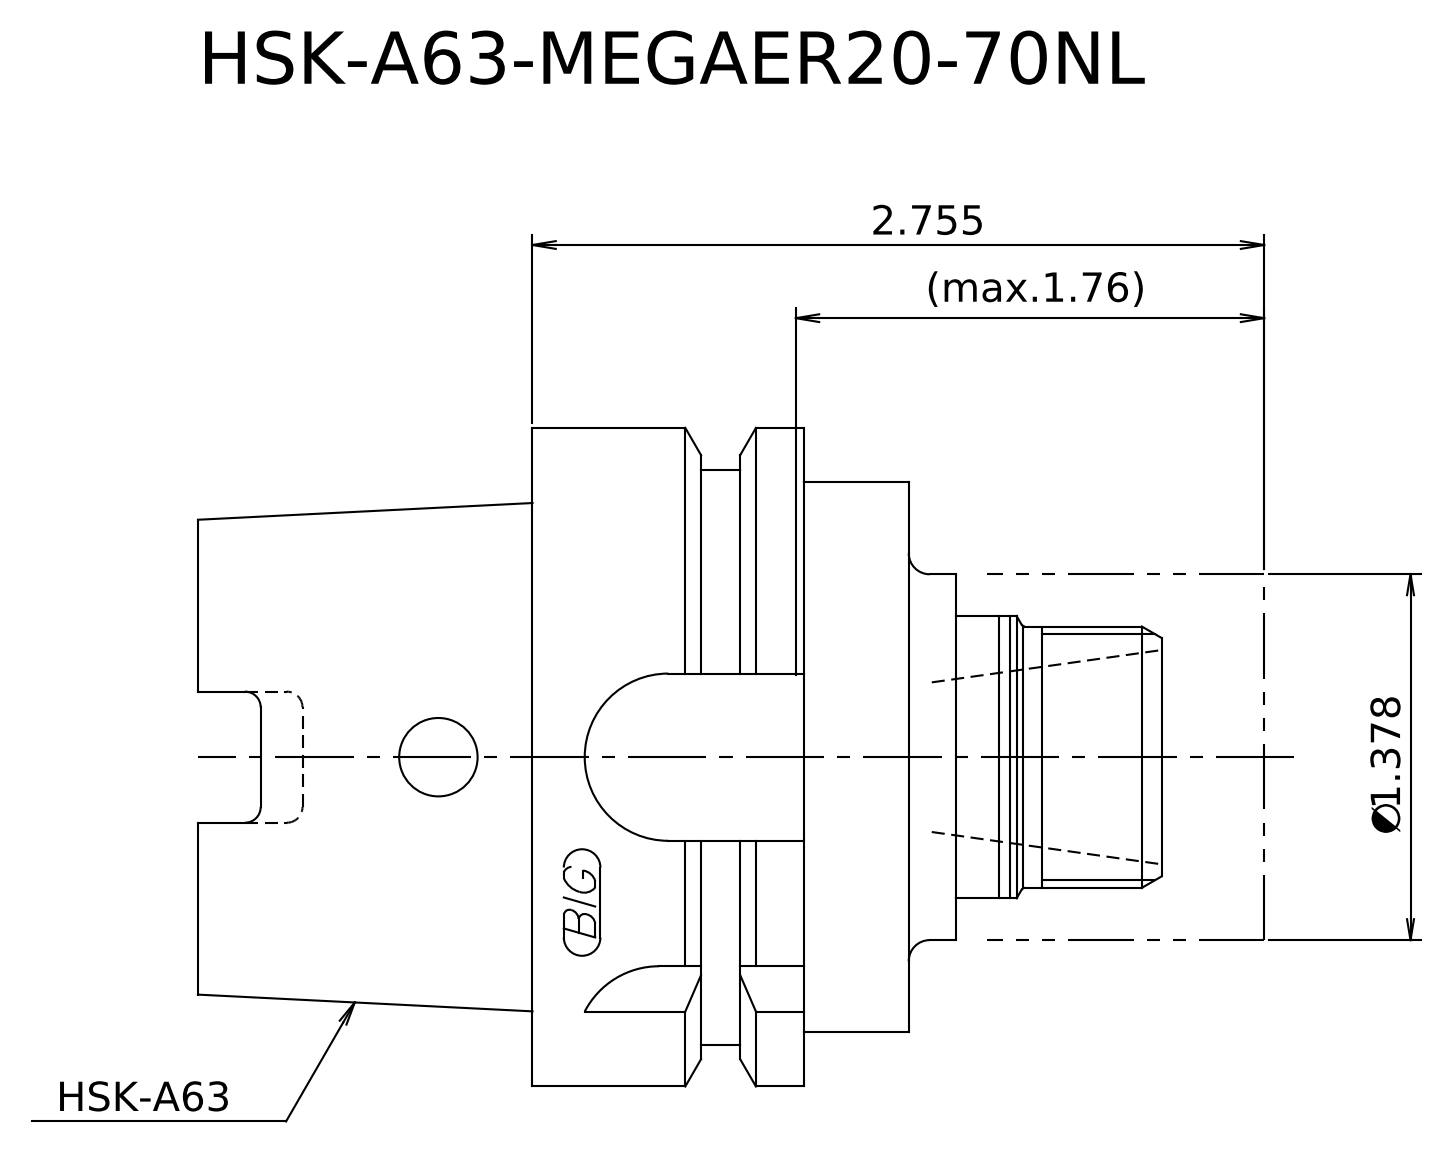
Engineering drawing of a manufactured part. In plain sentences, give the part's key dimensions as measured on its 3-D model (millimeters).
Its 3-D file was written by "Kubotek KeyCreator 2011 V10.0.2 (22737) (automotive_design)". It is 2 solids with 24 faces: 10 planar, 8 cylindrical and 6 other. Overall it measures 102 by 63 by 63 millimeters. Its volume is 194 999 cubic millimeters and its surface area 25 170 square millimeters. Round bosses or shafts: 1 of diameter 63, 1 of diameter 55, 1 of diameter 52.6, 1 of diameter 35, 1 of diameter 27, 1 of diameter 25. The main face-to-face distances are 32, 36, 68, 7.5, 43.5, 75.5, 26.5, 34, 70, 102.
